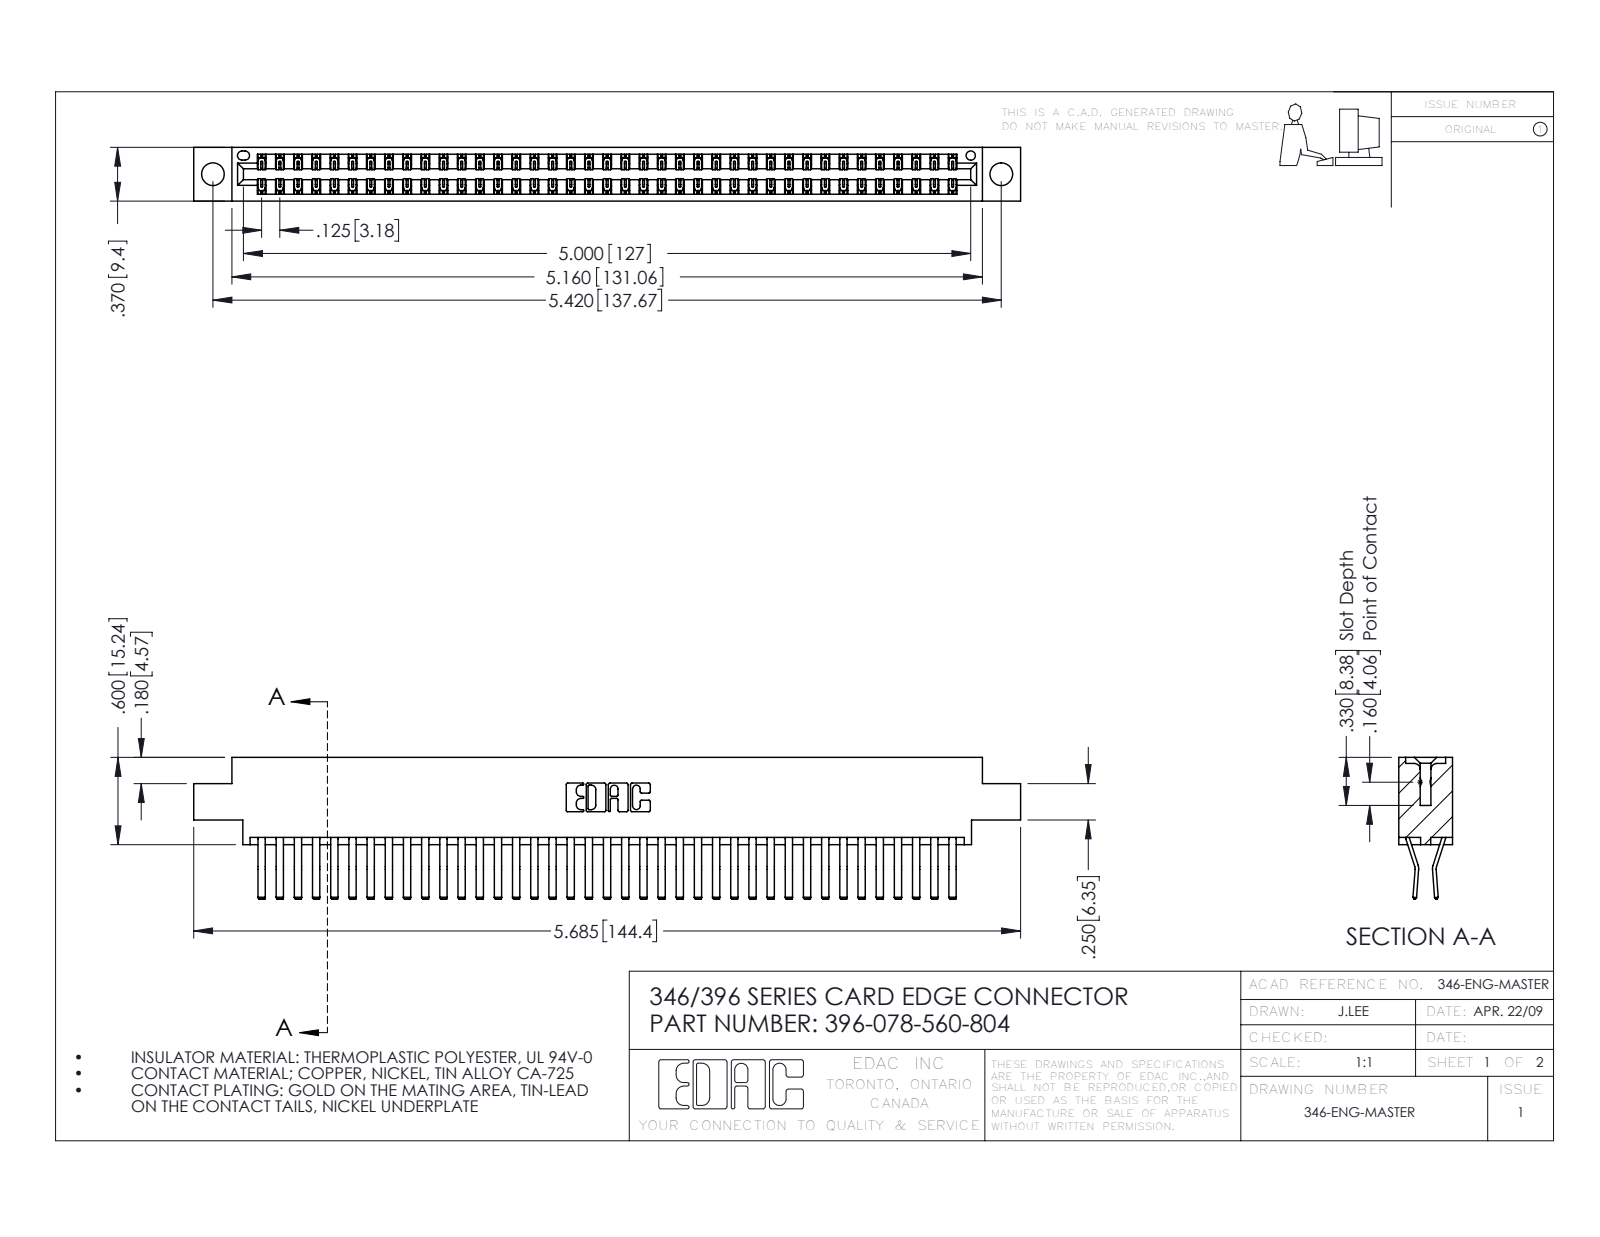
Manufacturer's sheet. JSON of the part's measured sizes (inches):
{"part_name": "346 Part_0.170 Offset - 0.156 Dia-TH; 396-078-560-804; 345-292-001_560 Tail", "step_written_by": "SolidWorks 2016 (CONFIG_CONTROL_DESIGN)", "units": "inches", "bodies": {"solids": 79, "faces": 4338, "planar": 2810, "cylindrical": 1528, "other": 0}, "overall_size": [5.685, 0.975, 0.37], "volume_in3": 0.874, "surface_area_in2": 32.55, "round_holes": [[0.156, 2], [0.064, 1]], "partial_cylinders_radius": [[0.006, 117], [0.01, 22], [0.007, 6], [0.031, 6], [0.026, 3], [0.01, 2], [0.014, 2], [0.022, 2]], "face_to_face_distances": [0.048, 0.322, 0.37, 0.025, 0.25, 0.072, 0.298, 0.275, 0.148, 0.222], "hole_center_spacings": [0.246, 5.211, 5.42]}
